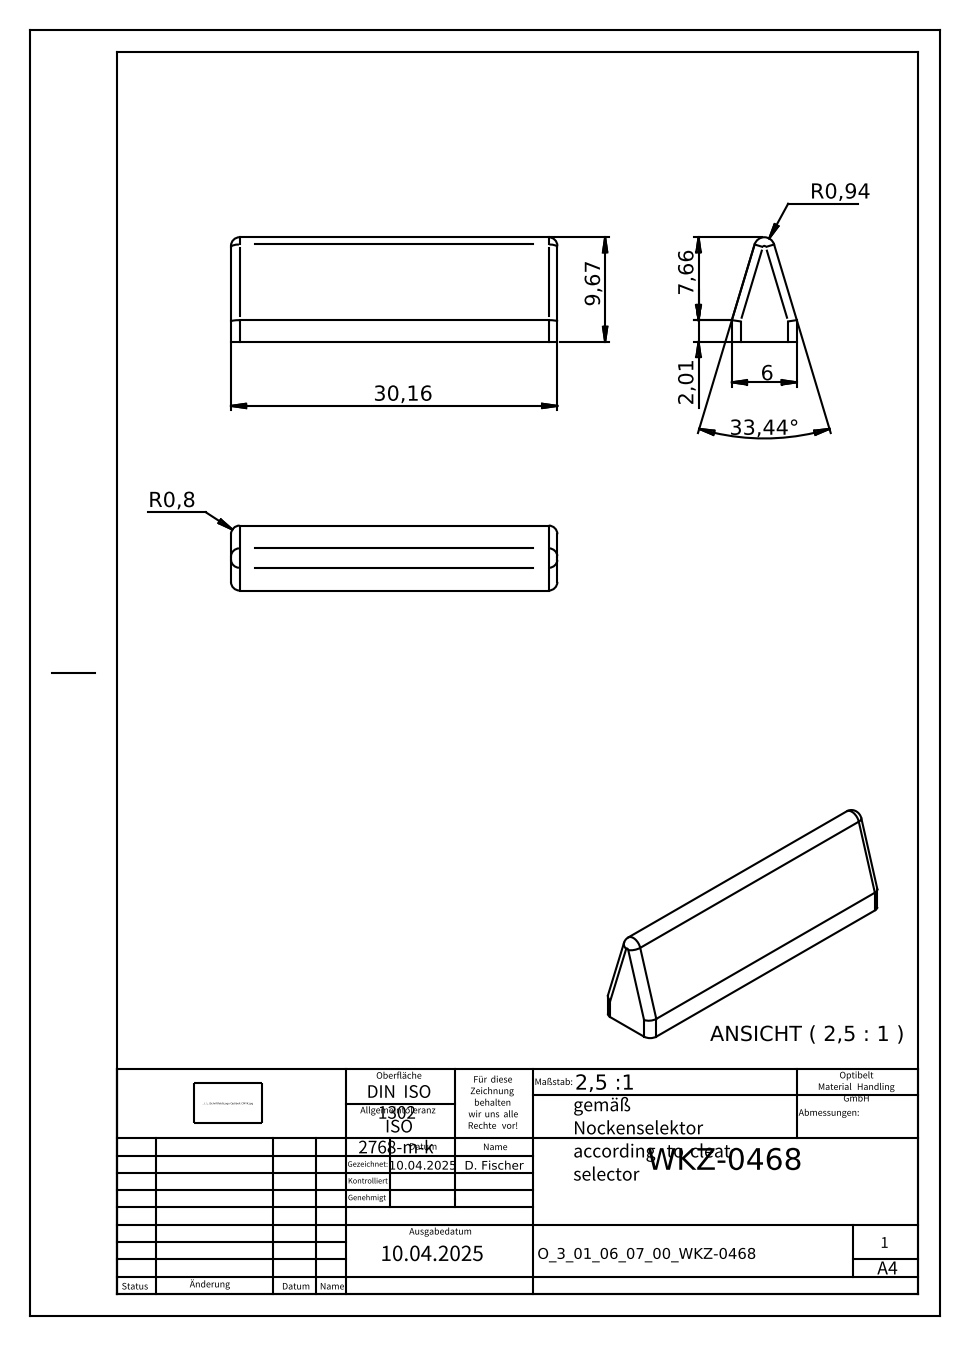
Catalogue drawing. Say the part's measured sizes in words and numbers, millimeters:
The part is named "O_3_01_06_07_00_WKZ-0468". Its 3-D file was written by "Autodesk Inventor 2025 (AUTOMOTIVE_DESIGN)". It is 1 solid with 18 faces: 7 planar, 9 cylindrical and 2 other. Overall it measures 30.16 by 9.67 by 6 millimeters. Its volume is 1 207 cubic millimeters and its surface area 880 square millimeters. Partial cylindrical surfaces (rounded edges, fillets, slot ends): 8 of radius 0.8, 1 of radius 0.94. The main face-to-face distances are 6, 30.16.
